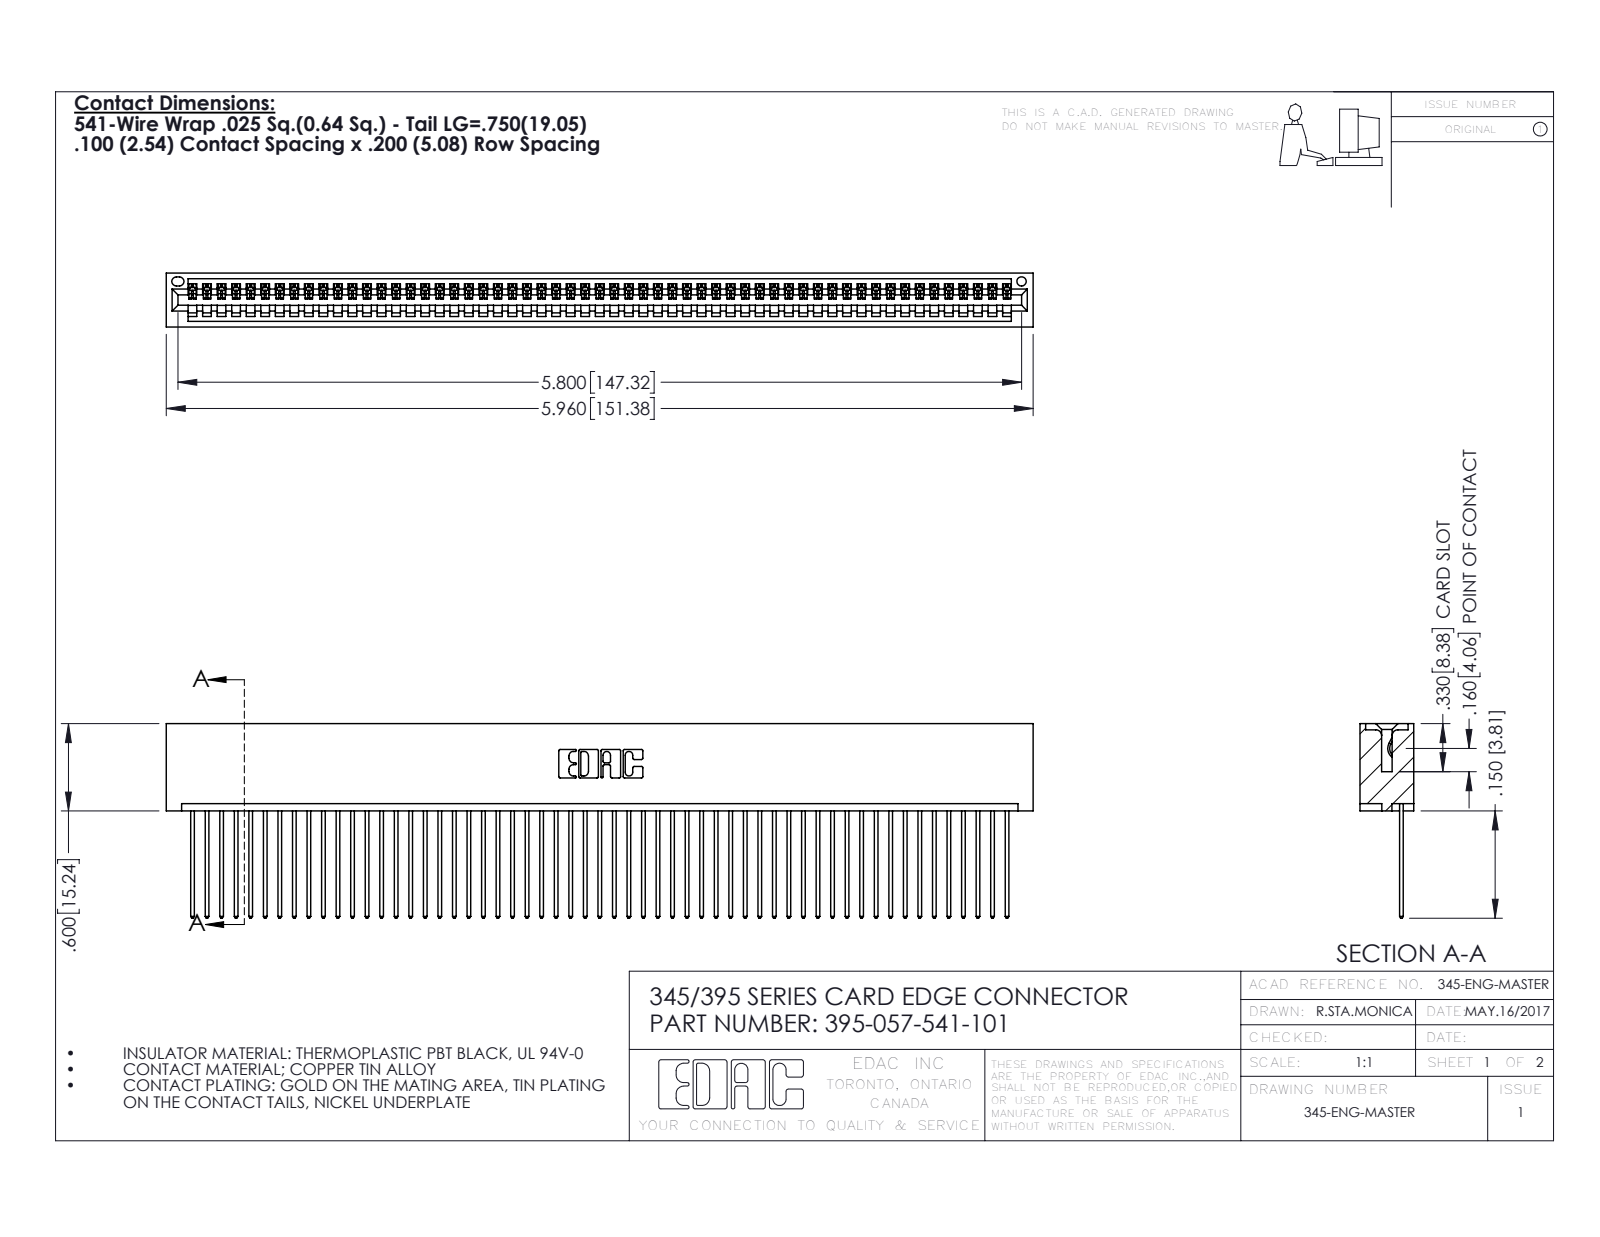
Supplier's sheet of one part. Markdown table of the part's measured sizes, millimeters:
| quantity | value |
| --- | --- |
| part name | 395-057-541-101; 345 Part_No Mounting Lugs; 345-292-001_345-293-141 |
| STEP written by | SolidWorks 2016 (CONFIG_CONTROL_DESIGN) |
| units | millimeters |
| bodies | 58 solids, 3424 faces (2356 planar, 1068 cylindrical, 0 other) |
| overall size | 151.4 × 34 × 9.4 |
| volume | 15 300 mm³ |
| surface area | 21 800 mm² |
| round holes (diameter × count) | 1.6 × 1 |
| partial cylindrical surfaces (radius × count) | 0.2 × 114, 0.3 × 114, 0.3 × 22, 0.2 × 6, 0.8 × 6, 0.7 × 3, 0.8 × 2, 1 × 2 |
| main face-to-face distances | 1.8, 7.6, 2.5, 6.9, 0.6, 9.4, 5.1, 5.7, 3.8, 1.8 |
